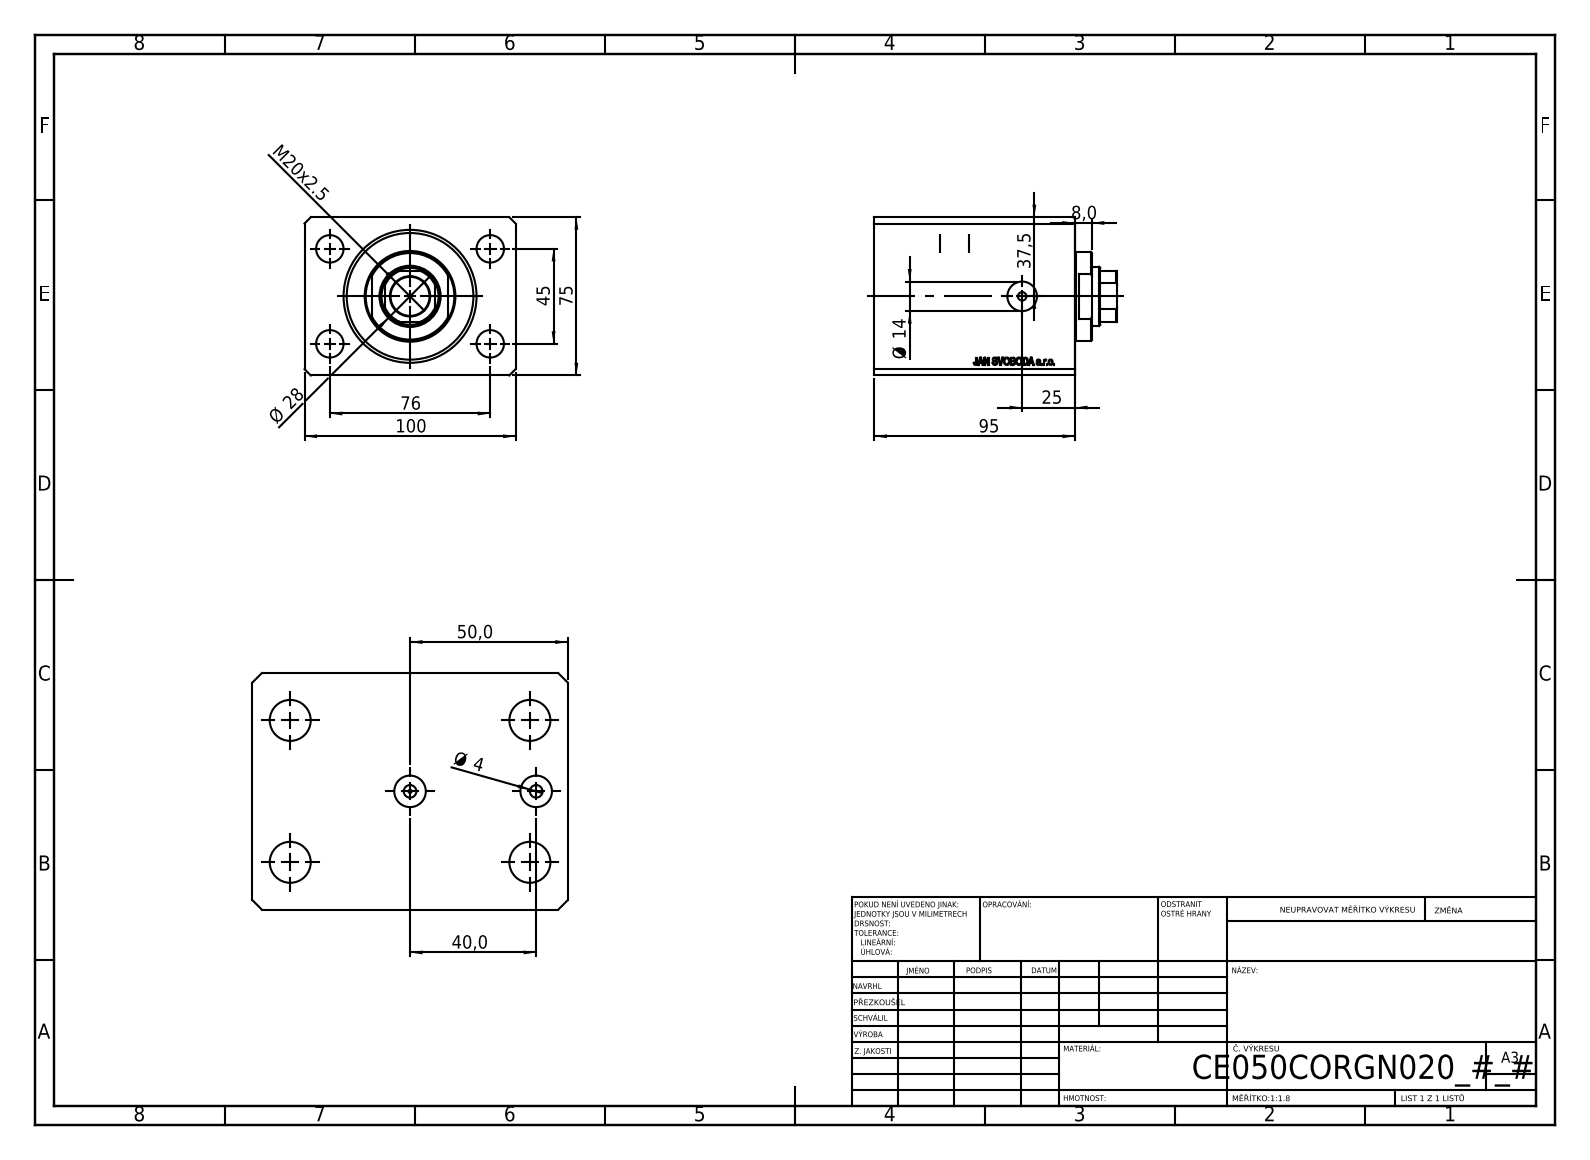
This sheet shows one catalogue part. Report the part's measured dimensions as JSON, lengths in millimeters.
{"part_name": "V250CE_C_Body; V250CE_C_VCP; V250CE_VC_C", "step_written_by": "SolidWorks 2019 (CONFIG_CONTROL_DESIGN)", "units": "millimeters", "bodies": {"solids": 3, "faces": 868, "planar": 428, "cylindrical": 46, "other": 394}, "overall_size": [115, 100, 75], "volume_mm3": 637305, "surface_area_mm2": 108736, "round_holes": [[4, 4], [13, 4], [10, 2], [14, 2], [1.25, 1], [18.5, 1], [28, 1], [50, 1], [63, 1]], "round_bosses_or_shafts": [[42, 1]], "partial_cylinders_radius": [[13.5, 1]], "face_to_face_distances": [75, 100, 95, 20, 11.9, 83.1, 63.1, 40, 55, 43.1], "hole_center_spacings": [44.16, 45, 22.59, 76, 81.18, 88.32, 40]}
